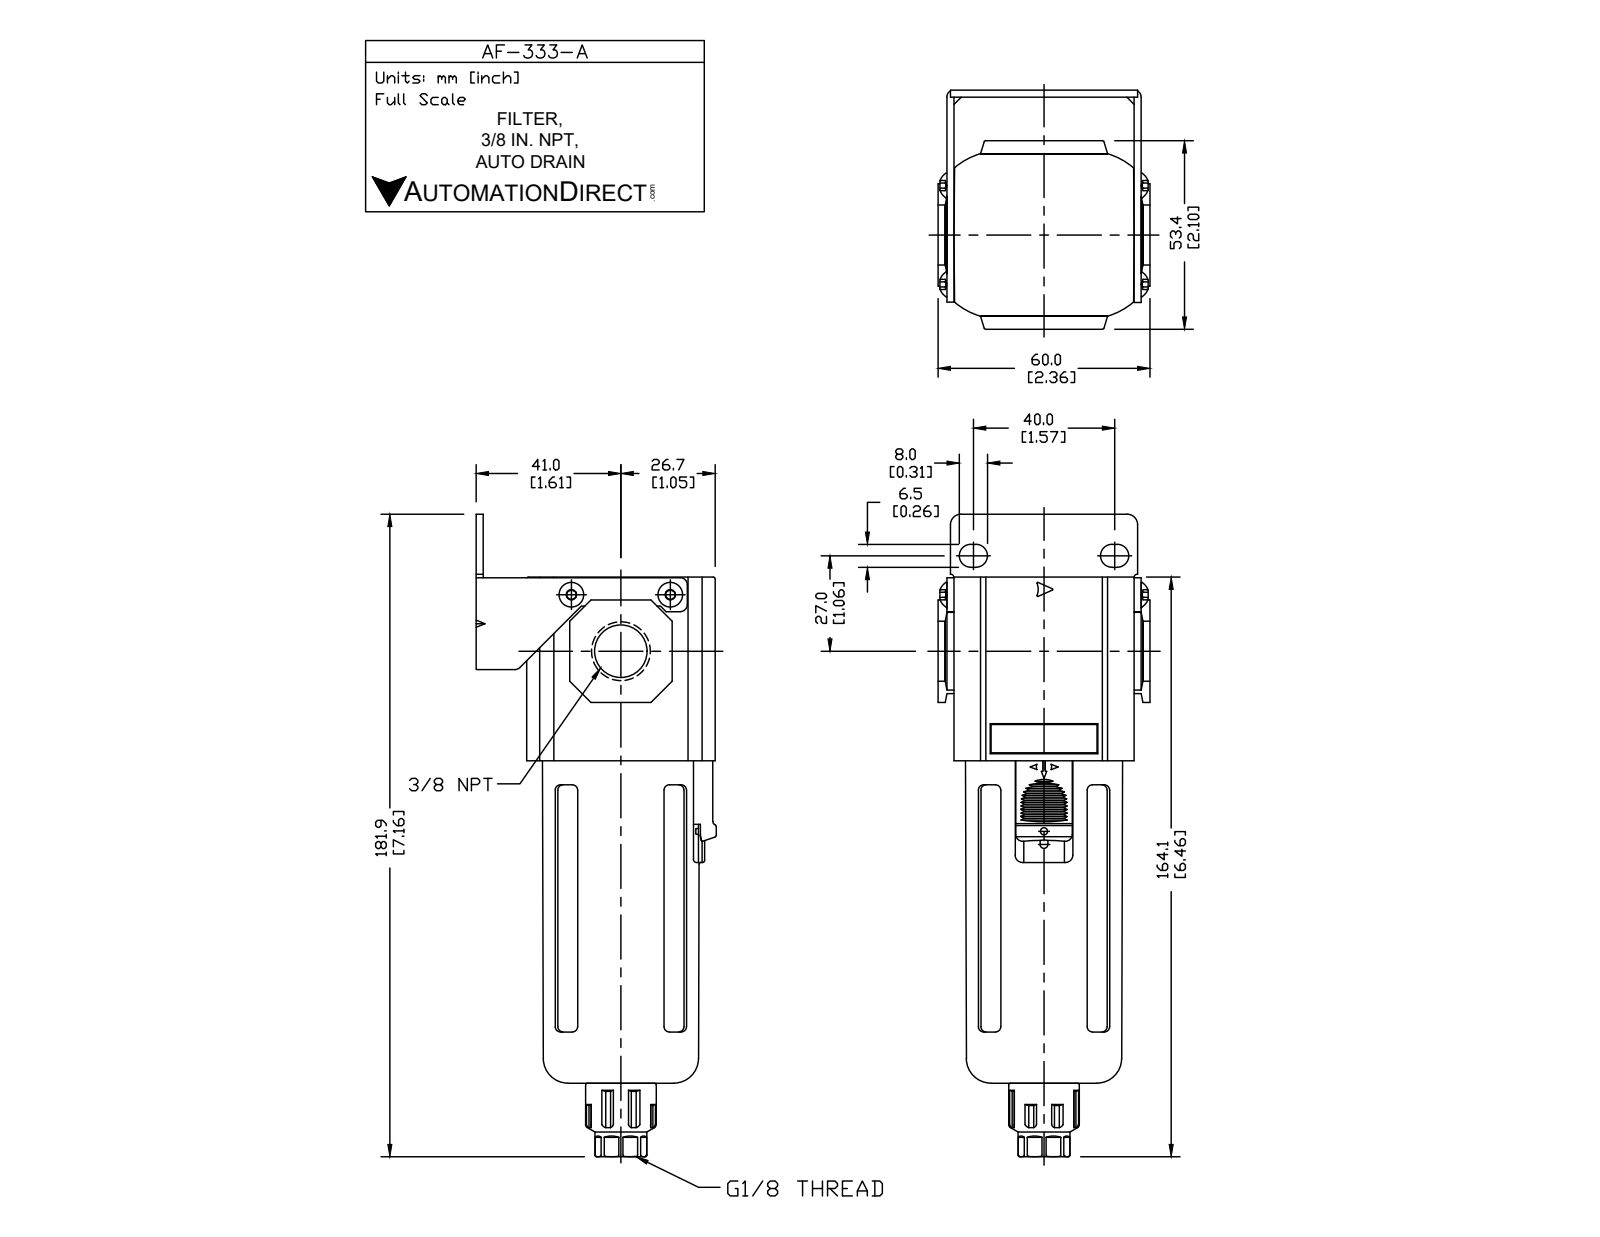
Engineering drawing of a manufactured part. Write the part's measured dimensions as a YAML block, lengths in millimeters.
part_name: "AF-333-A"
step_written_by: "SolidWorks 2015 (CONFIG_CONTROL_DESIGN)"
units: millimeters
bodies: {solids: 9, faces: 394, planar: 246, cylindrical: 94, other: 54}
overall_size: [182.3, 67.7, 60]
volume: 203276
surface_area: 60945
round_holes:
  - {diameter: 3.4, count: 2}
  - {diameter: 8.57, count: 1}
  - {diameter: 14.27, count: 1}
  - {diameter: 35.99, count: 1}
  - {diameter: 44.8, count: 1}
round_bosses_or_shafts:
  - {diameter: 44.47, count: 1}
  - {diameter: 26, count: 1}
  - {diameter: 22.24, count: 1}
  - {diameter: 14.82, count: 1}
partial_cylinders:
  - {radius: 1, count: 18}
  - {radius: 2, count: 8}
  - {radius: 9.5, count: 8}
  - {radius: 0.5, count: 6}
  - {radius: 0.3, count: 4}
  - {radius: 3.25, count: 4}
  - {radius: 20, count: 4}
  - {radius: 0.2, count: 3}
face_to_face_distances: [2, 51, 53, 2.5, 12.3, 67.7, 65.7, 14.3, 53.4, 55.5]
hole_center_spacings: [21.06, 21.46, 28]
